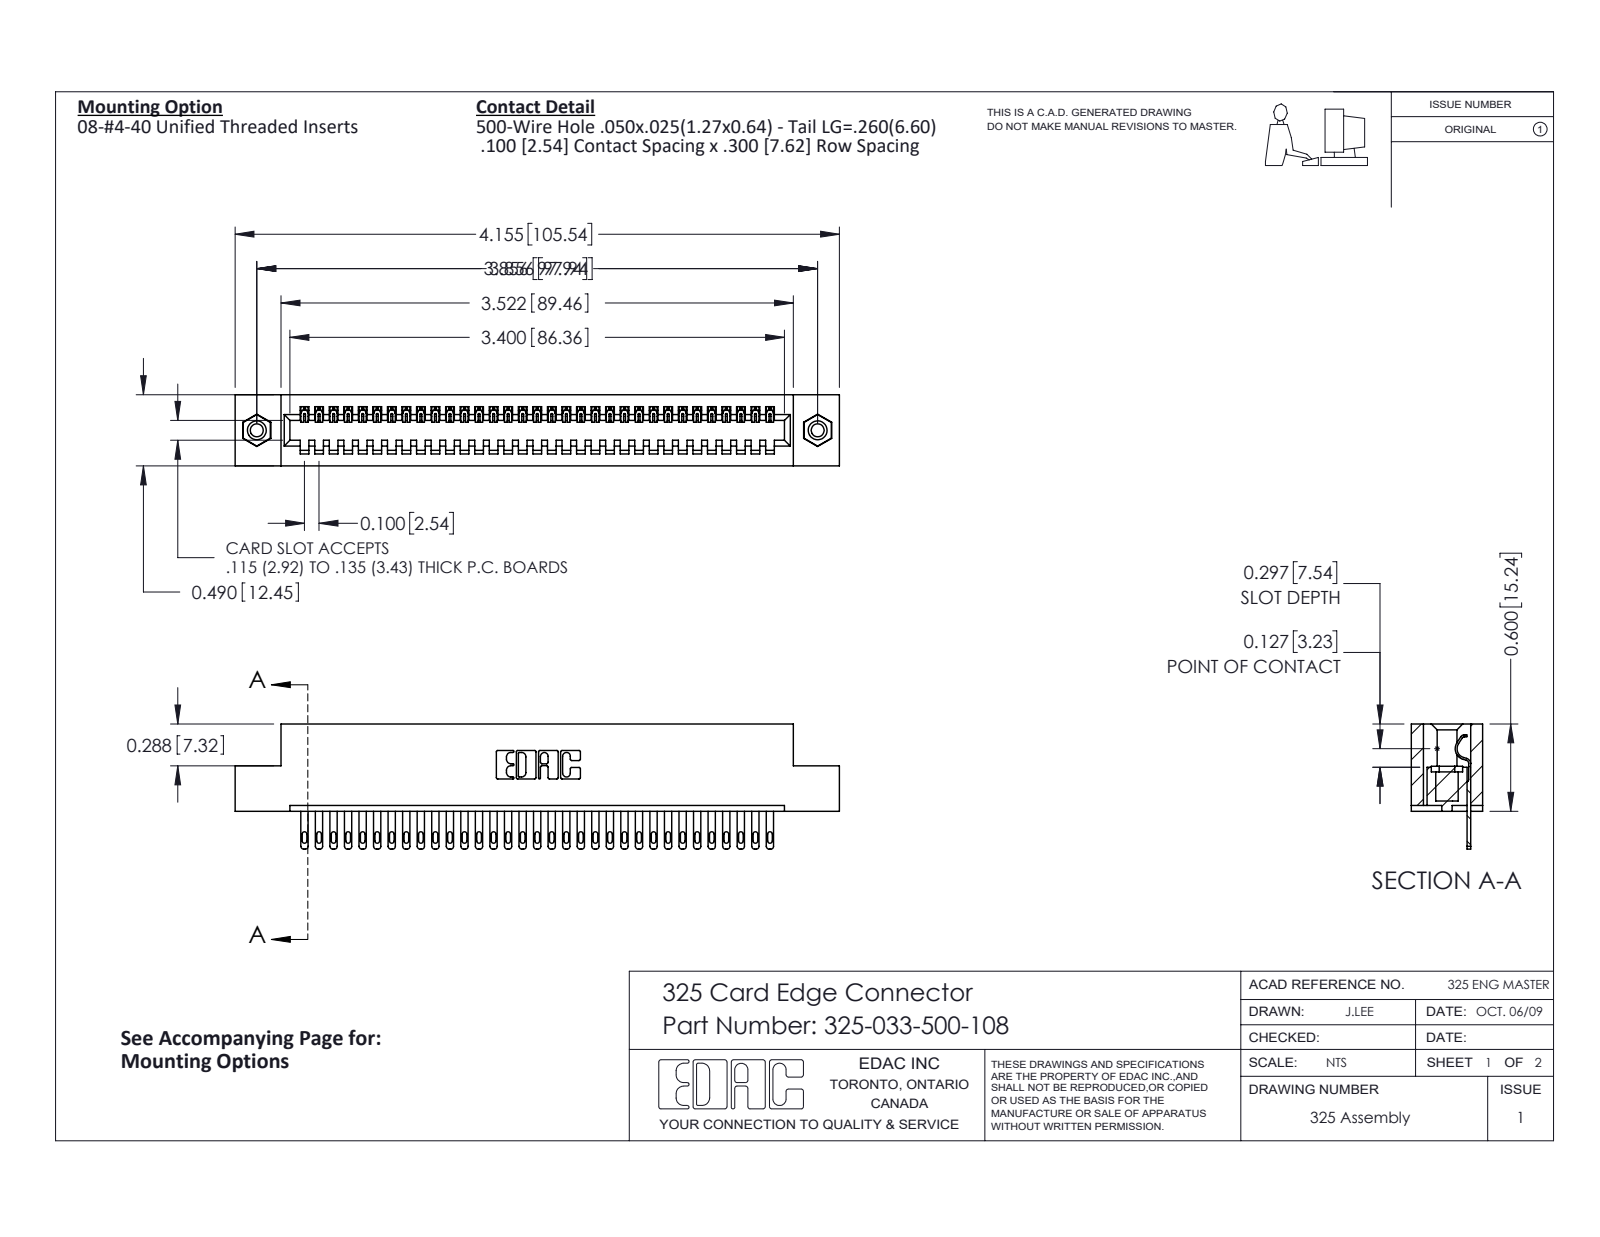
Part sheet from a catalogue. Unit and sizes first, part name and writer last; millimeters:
Units: millimetres
Overall size (bounding box): 105.5 × 21.8 × 12.4
Round holes (diameter × count): ⌀2.3 ×2, ⌀3.2 ×2, ⌀4.1 ×2
Round bosses / shafts (diameter × count): ⌀3.9 ×2
Partial cylindrical surfaces — rounded edges, fillets, slot ends (radius × count): R0.2 ×66, R0.4 ×66, R0.5 ×66, R0.3 ×22, R0.2 ×6, R0.8 ×6, R0.7 ×3, R0.4 ×1
Main face-to-face distances: 2.1, 10.3, 12.4, 7.6, 2.7, 9.7, 0.6, 8.3, 14.2, 1
Hole centre spacings: 97.9
Volume: 13 300 mm³ · Surface area: 14 520 mm²
Bodies: 36 solids, 1956 faces (1290 planar, 650 cylindrical, 16 other)
Part name (STEP PRODUCT): 325 Part_TI; 325-033-500-108; 345-250-001_345-250-003-102; 325-292-001_325-293-100
STEP written by: SolidWorks 2016 (CONFIG_CONTROL_DESIGN)
